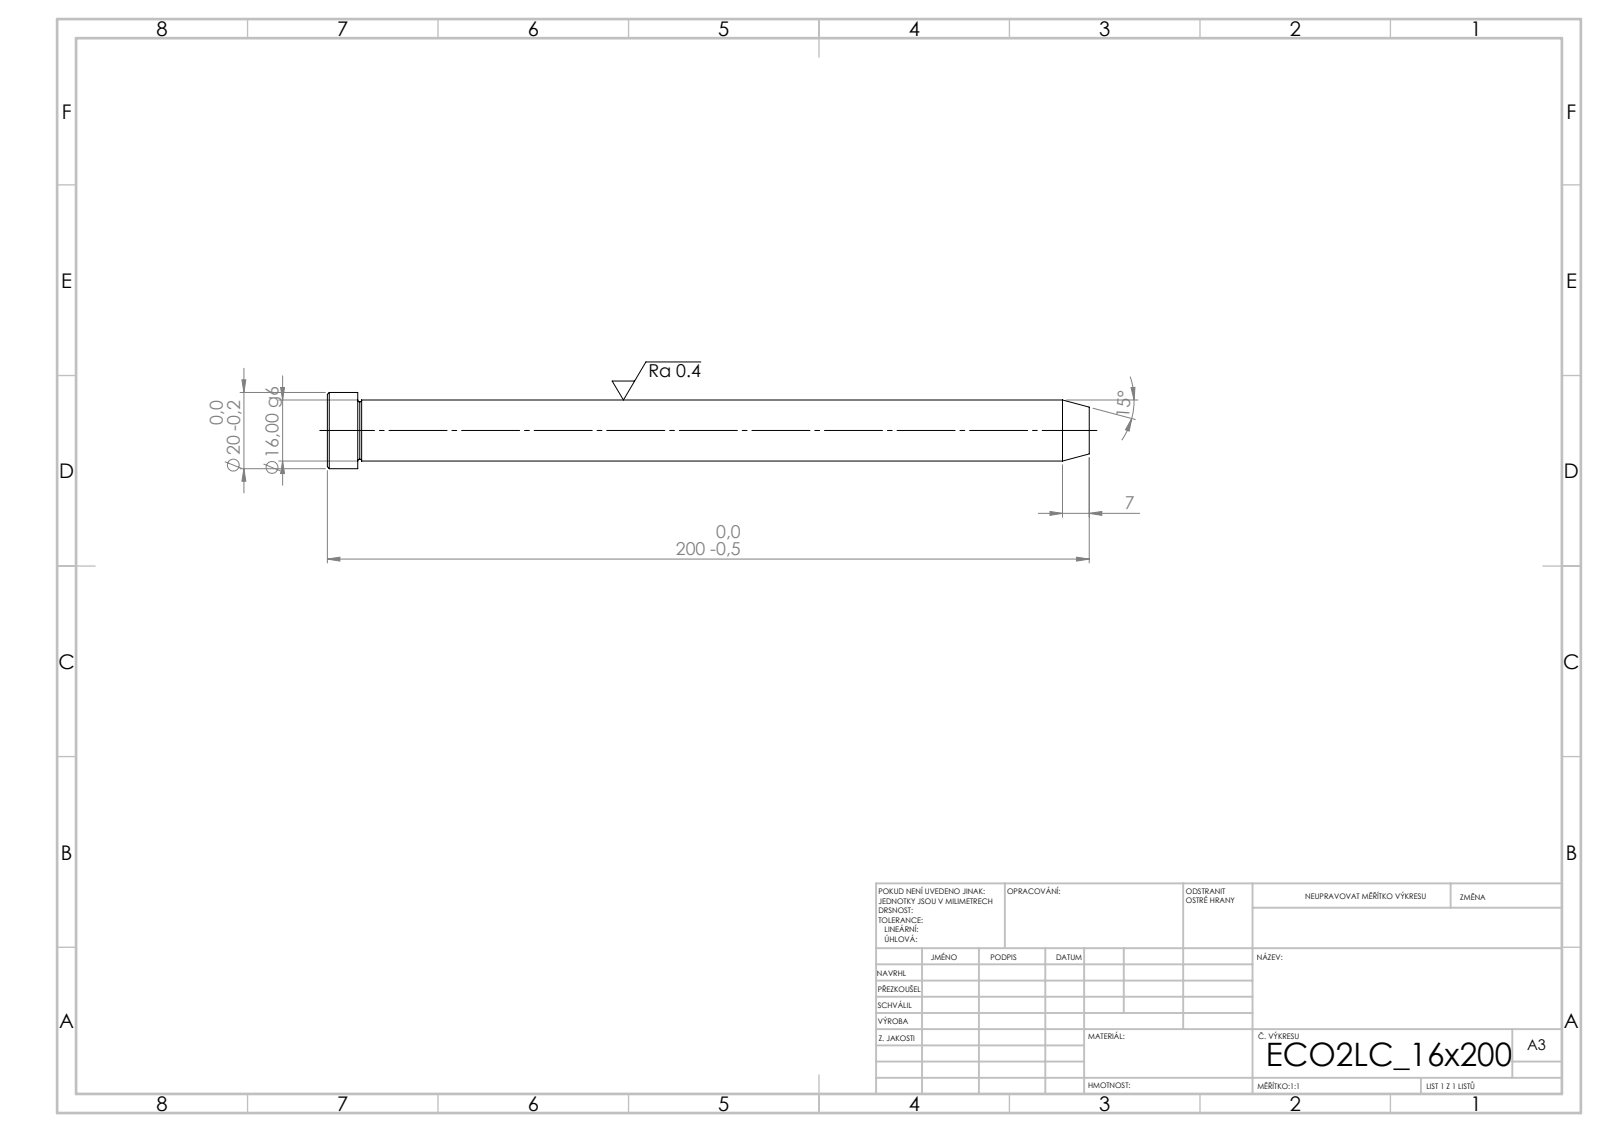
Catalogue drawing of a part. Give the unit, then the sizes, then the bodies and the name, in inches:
Units: inches
Overall size (bounding box): 7.874 × 0.787 × 0.787
Round bosses / shafts (diameter × count): ⌀0.787 ×1, ⌀0.63 ×1
Main face-to-face distances: 7.874, 7.559, 0.315
Volume: 2.489 in³ · Surface area: 16.55 in²
Bodies: 1 solid, 15 faces (3 planar, 4 cylindrical, 8 other)
STEP written by: SolidWorks 2019 (CONFIG_CONTROL_DESIGN)
